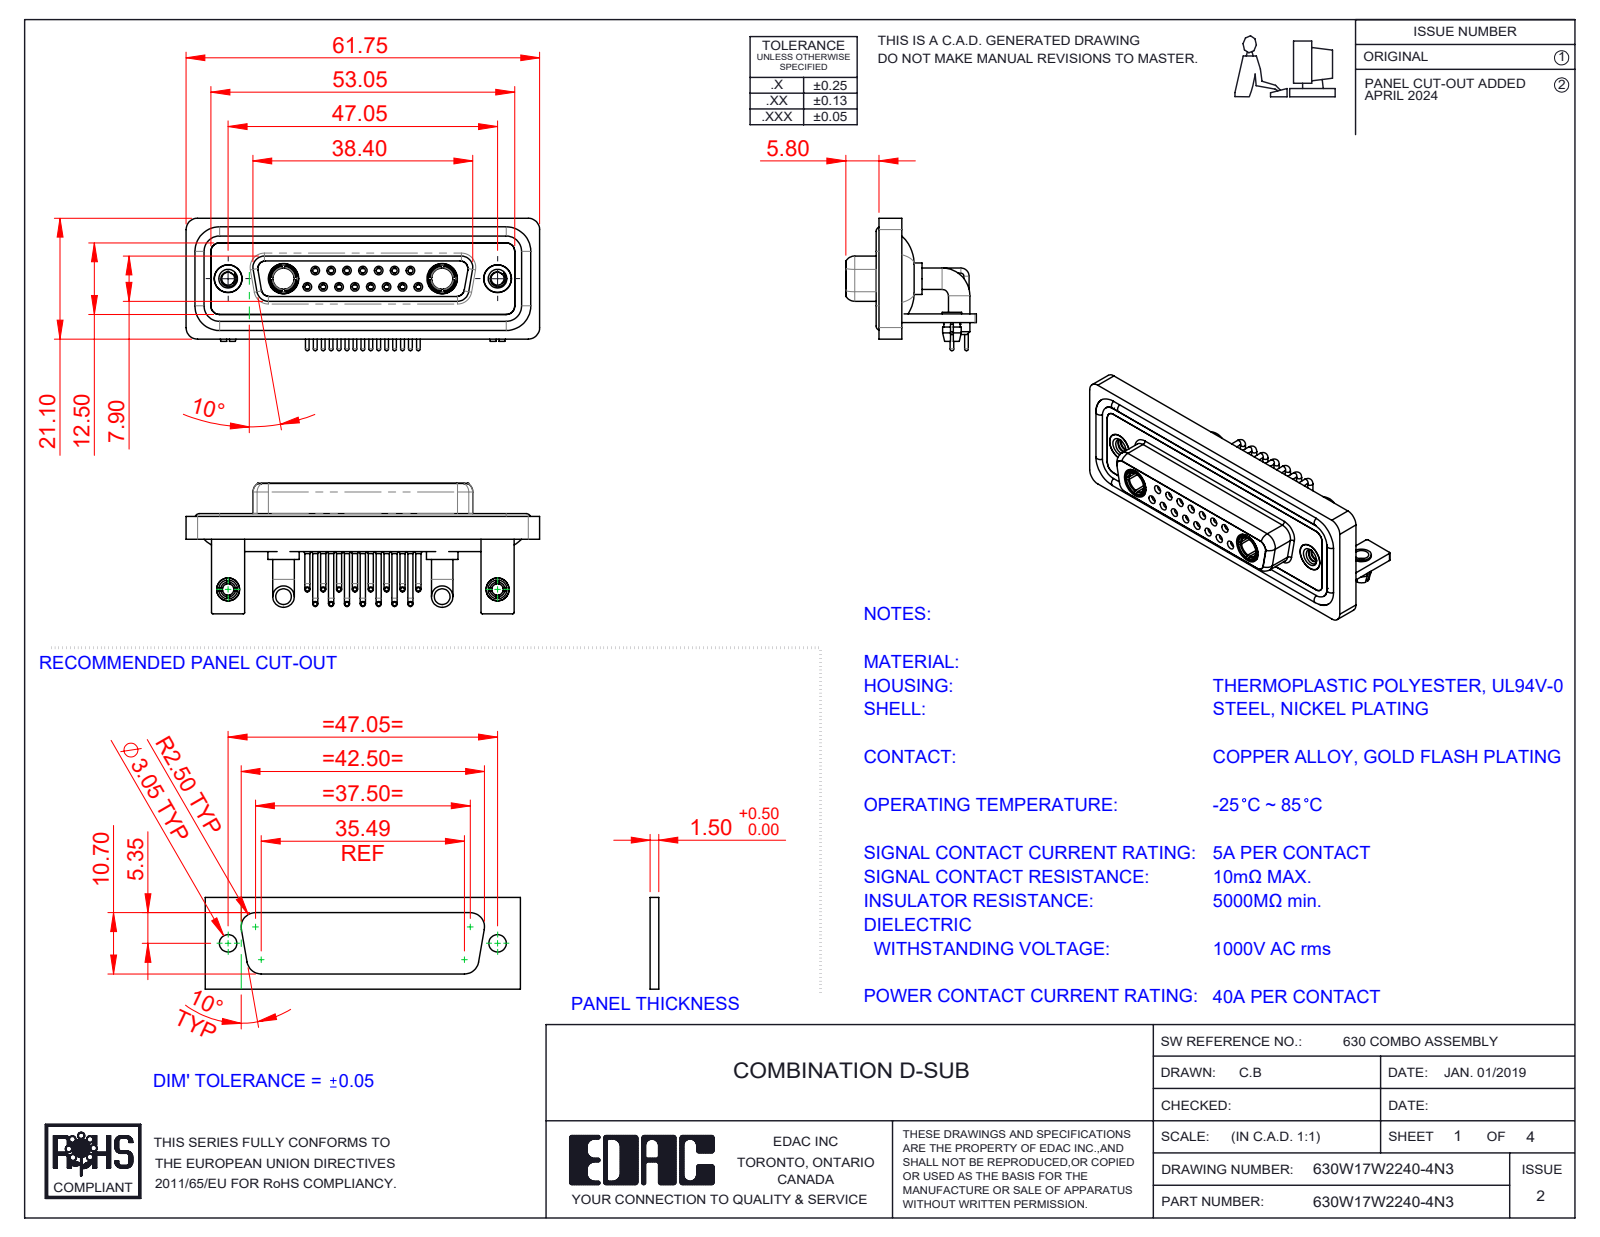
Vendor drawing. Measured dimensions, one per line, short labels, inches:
name: 630Combo Housing_17W2; 630Combo Shell Rear_25 Contacts; 630Combo Contact Row 2_50 Contacts; 630Combo Threaded Rivet_2 (+7 more)
written by: SolidWorks 2023 (CONFIG_CONTROL_DESIGN)
unit: in
bodies: 30 solids, 1477 faces (456 planar, 639 cylindrical, 382 other)
size: 2.431 × 0.91 × 0.898
volume: 0.551 in³; area: 24.12 in²
holes: 17× ⌀0.079, 15× ⌀0.035, 15× ⌀0.043, 15× ⌀0.059, 8× ⌀0.063, 7× ⌀0.067, 4× ⌀0.191, 2× ⌀0.089, 2× ⌀0.098, 2× ⌀0.126, 2× ⌀0.146, 2× ⌀0.157
bosses: 15× ⌀0.035, 15× ⌀0.026, 11× ⌀0.063, 4× ⌀0.148, 2× ⌀0.217, 2× ⌀0.205, 2× ⌀0.195, 2× ⌀0.195
rounds: 19× R0.079, 18× R0.059, 16× R0.01, 8× R0.053, 8× R0.063, 5× R0.02, 4× R0.024, 4× R0.026
face distances: 0.016, 0.071, 0.114, 0.146, 0.059, 0.161, 0.043, 0.055, 0.063, 0.122
hole spacings: 0.124, 0.109, 0.218, 0.327, 0.198, 0.295, 0.436, 0.198
